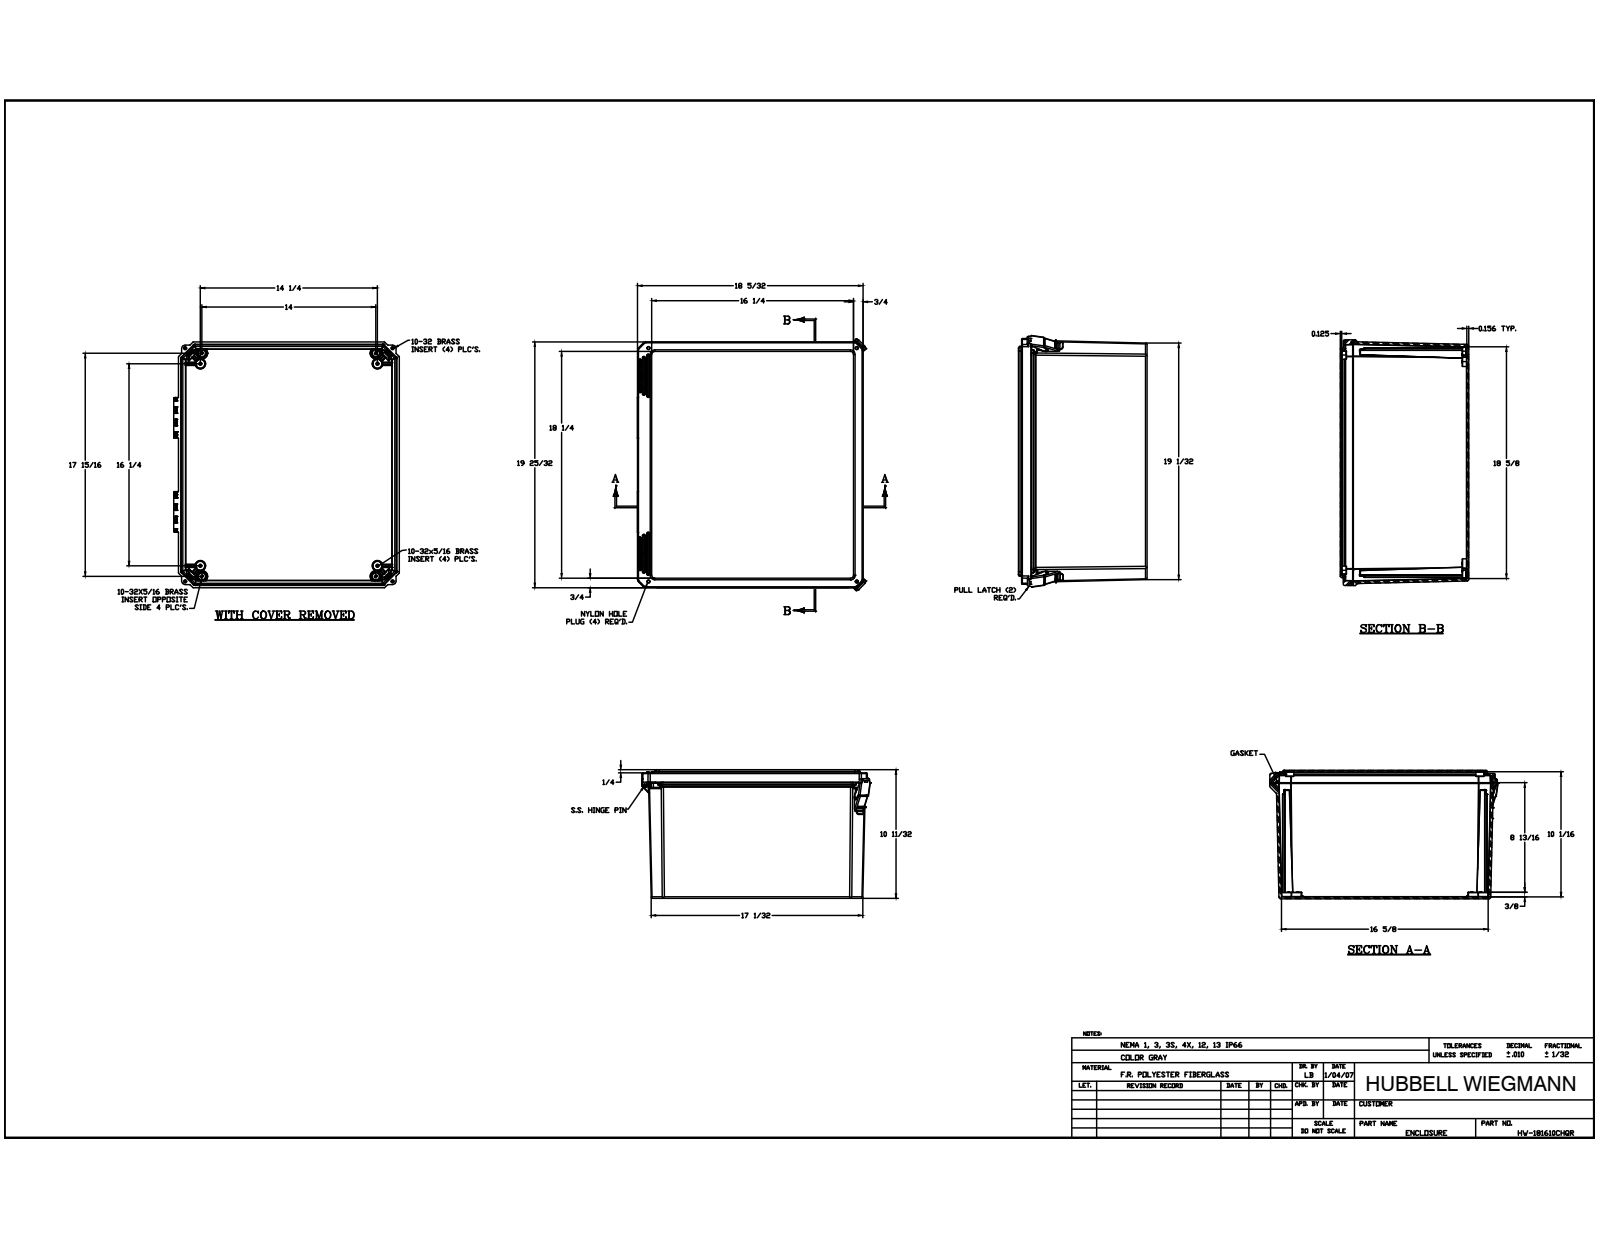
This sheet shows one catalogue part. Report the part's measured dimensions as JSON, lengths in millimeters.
{"part_name": "DS181610BOX; BRASS INSERT-(; BRASS INSERT-(_1; BRASS INSERT-(_2 (+6 more)", "step_written_by": "Autodesk Inventor 2014 (AUTOMOTIVE_DESIGN)", "units": "millimeters", "bodies": {"solids": 35, "faces": 2616, "planar": 914, "cylindrical": 1046, "other": 656}, "overall_size": [516.85, 468.37, 262.67], "volume_mm3": 4265000, "surface_area_mm2": 1924000, "round_holes": [[3.96, 16], [3.43, 9], [3.86, 8], [3.81, 4], [6.4, 4], [6.43, 4], [3.43, 2], [5.56, 2], [5.77, 2], [7.94, 2], [9.52, 2], [3.48, 1]], "round_bosses_or_shafts": [[6.25, 16], [7.62, 4], [5.3, 4], [11.05, 2], [3.43, 1]], "partial_cylinders_radius": [[0.25, 205], [0.51, 111], [0.13, 88], [0.76, 59], [1.52, 35], [1.59, 26], [2.29, 26], [0.76, 24]], "face_to_face_distances": [3.17, 3.96, 258.71, 262.67, 5.13, 5.08, 259.5, 255.54, 6.35, 3.18], "hole_center_spacings": [6.35, 45.28, 36.73, 359.41, 395.27, 594.16, 608.39, 21.74]}
